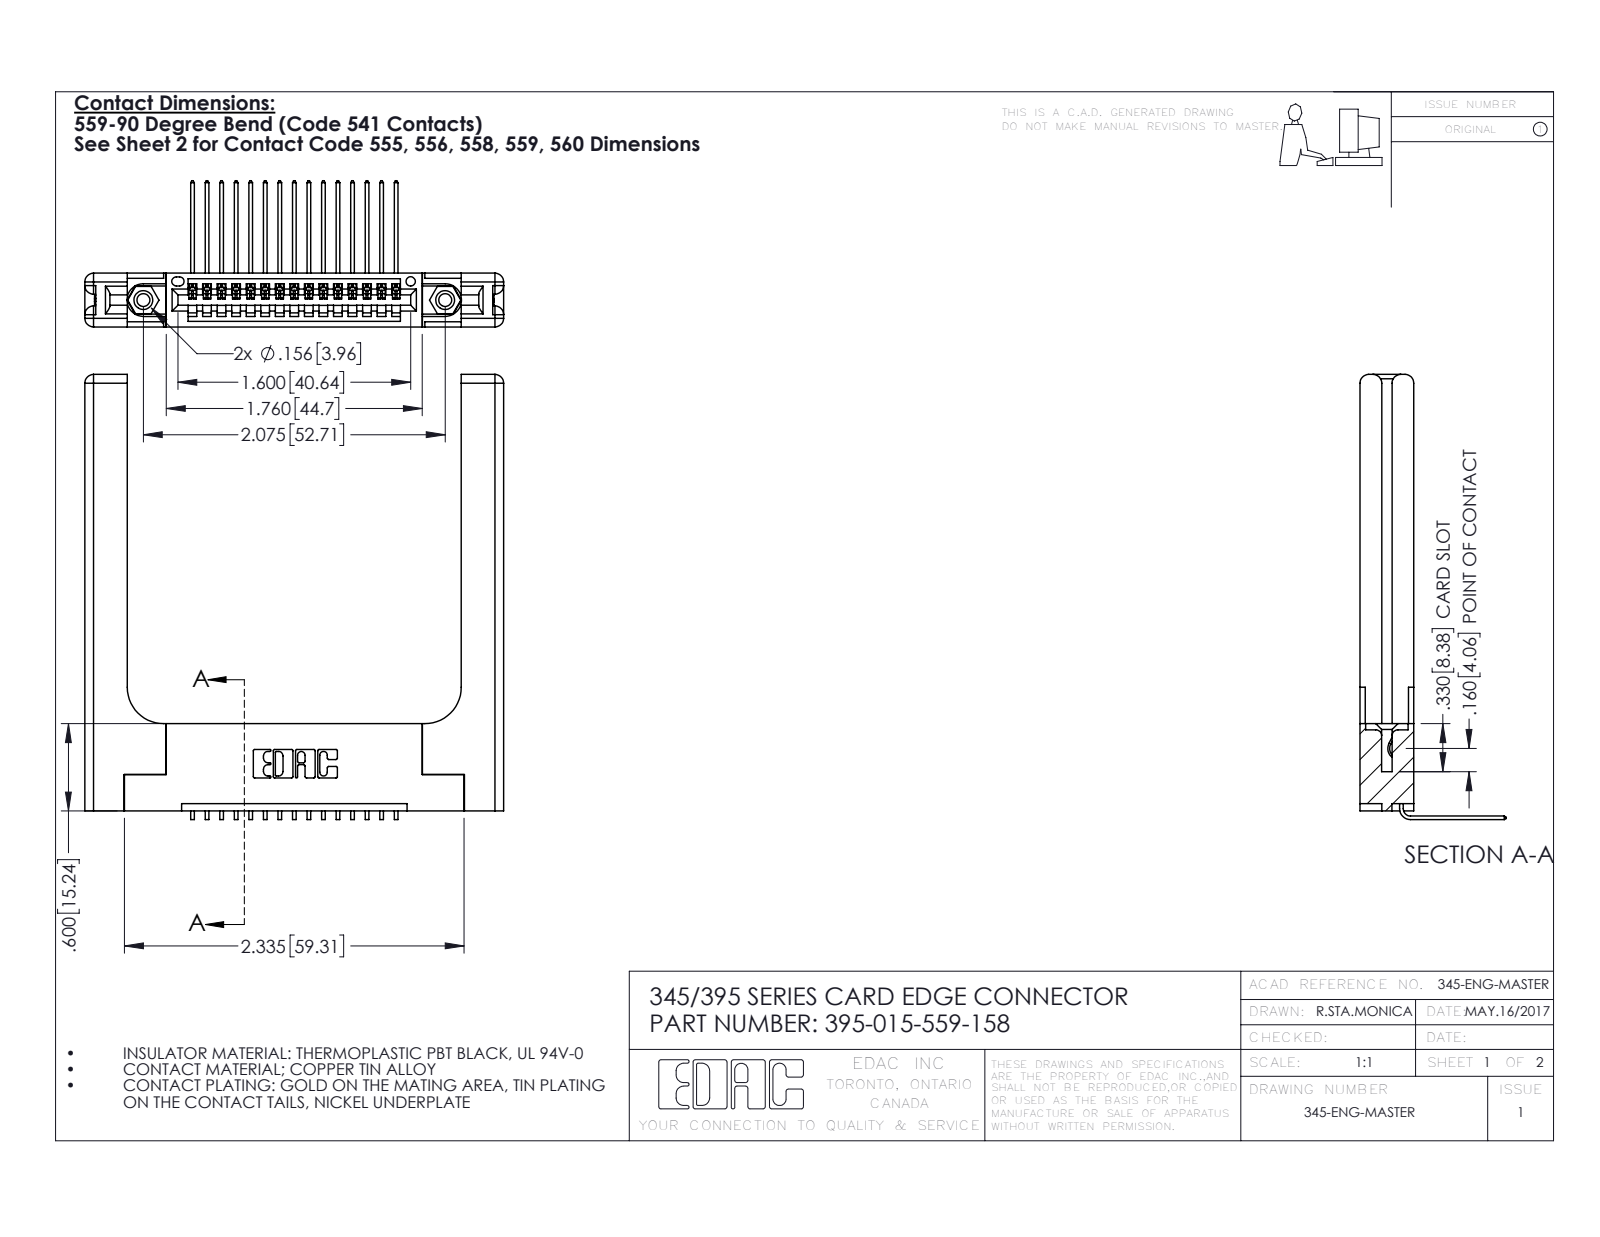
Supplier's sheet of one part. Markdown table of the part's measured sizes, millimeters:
| quantity | value |
| --- | --- |
| part name | 345-250-001_345-250-001-102; 345-292-001_558 559 Tail - 1; 345-220-058_345-220-058; 395-015-559-158 (+1 more) |
| STEP written by | SolidWorks 2016 (CONFIG_CONTROL_DESIGN) |
| units | millimeters |
| bodies | 20 solids, 1282 faces (858 planar, 364 cylindrical, 60 other) |
| overall size | 77.7 × 73.1 × 25.5 |
| volume | 15 300 mm³ |
| surface area | 14 230 mm² |
| round holes (diameter × count) | 2.3 × 2, 3.2 × 2, 4 × 2, 1.6 × 1 |
| round bosses / shafts (diameter × count) | 3.9 × 2 |
| partial cylindrical surfaces (radius × count) | 0.2 × 30, 0.3 × 22, 1.5 × 16, 0.2 × 6, 0.8 × 6, 0.7 × 3, 0.8 × 2, 0.8 × 2 |
| main face-to-face distances | 9.4, 1.8, 7.6, 3.8, 2, 3.8, 5.6, 5.1, 58.3, 5.7 |
| hole center spacings | 6.9, 46.8, 52.7 |
